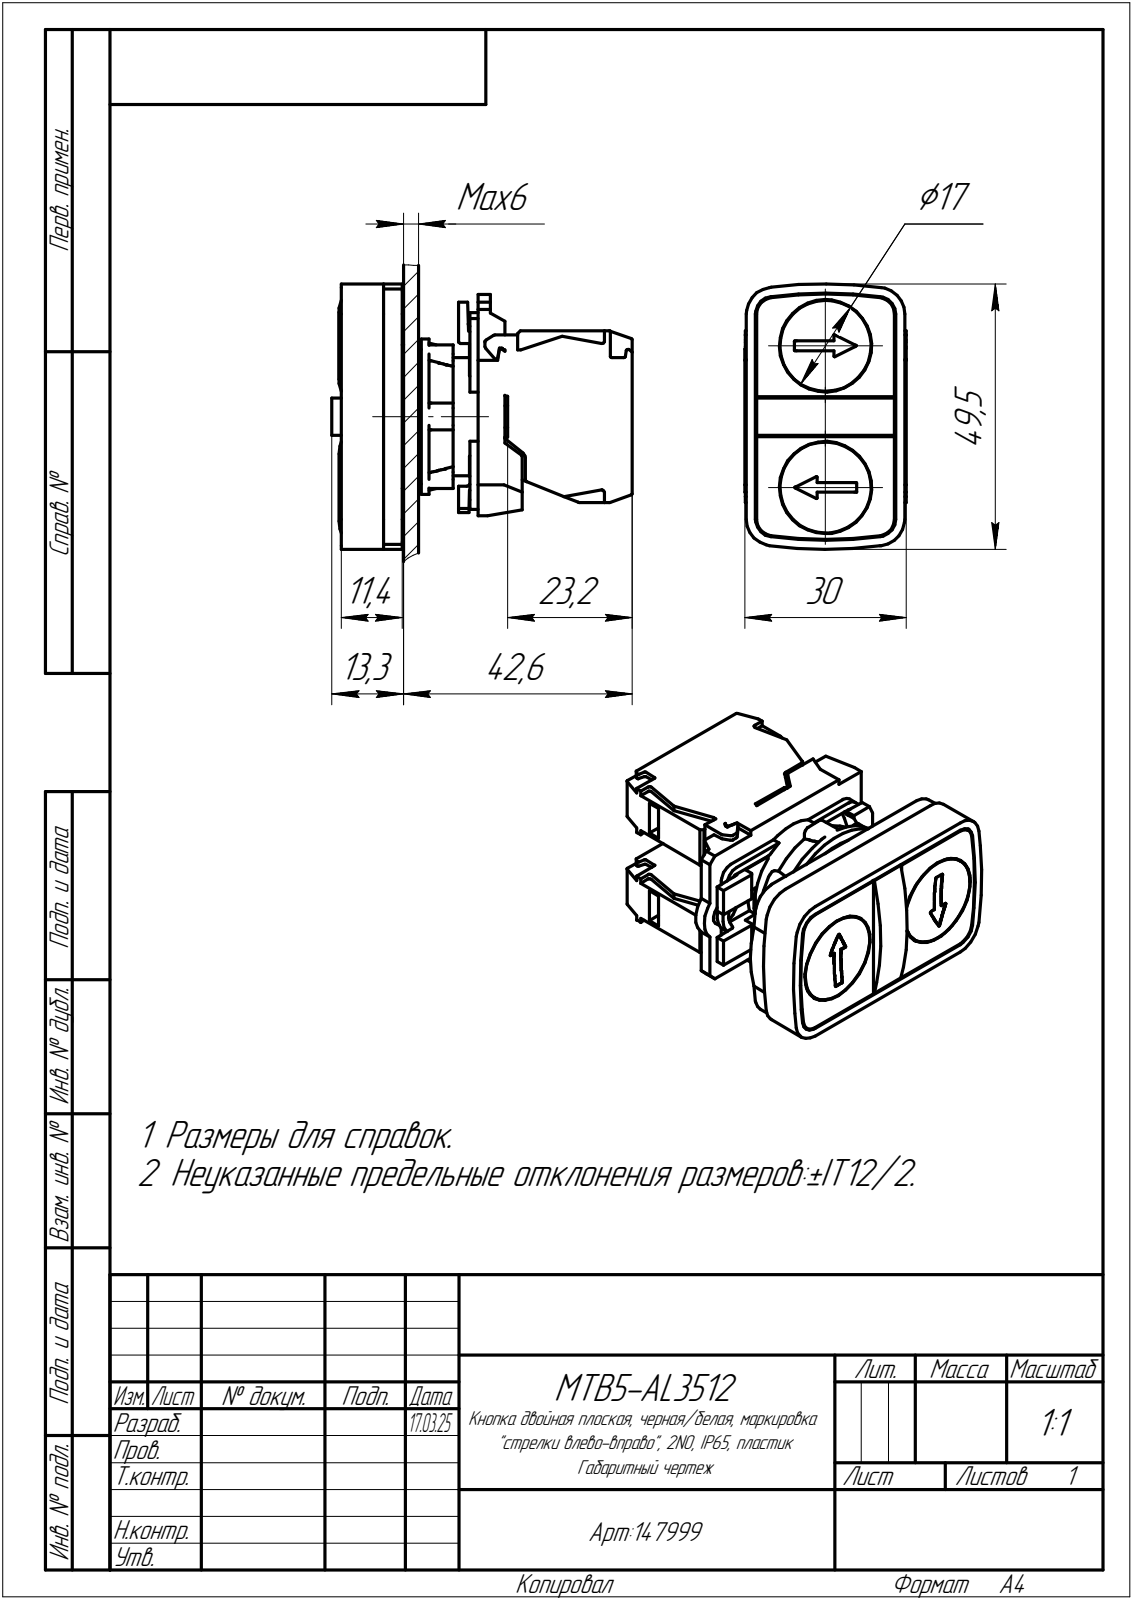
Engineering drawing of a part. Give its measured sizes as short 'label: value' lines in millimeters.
name: LA167-B5-ALA3512315
written by: PRO/ENGINEER BY PARAMETRIC TECHNOLOGY CORPORATION, 2010280 (CONFIG_CONTROL_DESIGN)
unit: mm
bodies: 1 solid, 545 faces (353 planar, 167 cylindrical, 25 other)
size: 55.9 × 49.5 × 30
volume: 41 341 mm³; area: 16 536 mm²
holes: 2× ⌀17.2, 1× ⌀5.2, 1× ⌀20.5
bosses: 2× ⌀17, 1× ⌀29, 1× ⌀26.8, 1× ⌀25, 1× ⌀22
rounds: 15× R1, 13× R0.2, 10× R0.1, 7× R0.5, 4× R2.5, 4× R3.1, 4× R3.3, 4× R4.35
face distances: 20, 9.9, 14.1, 25.5, 11.4, 10.1, 29.9, 9, 27.8, 1.7
hole spacings: 13.2, 26.4
